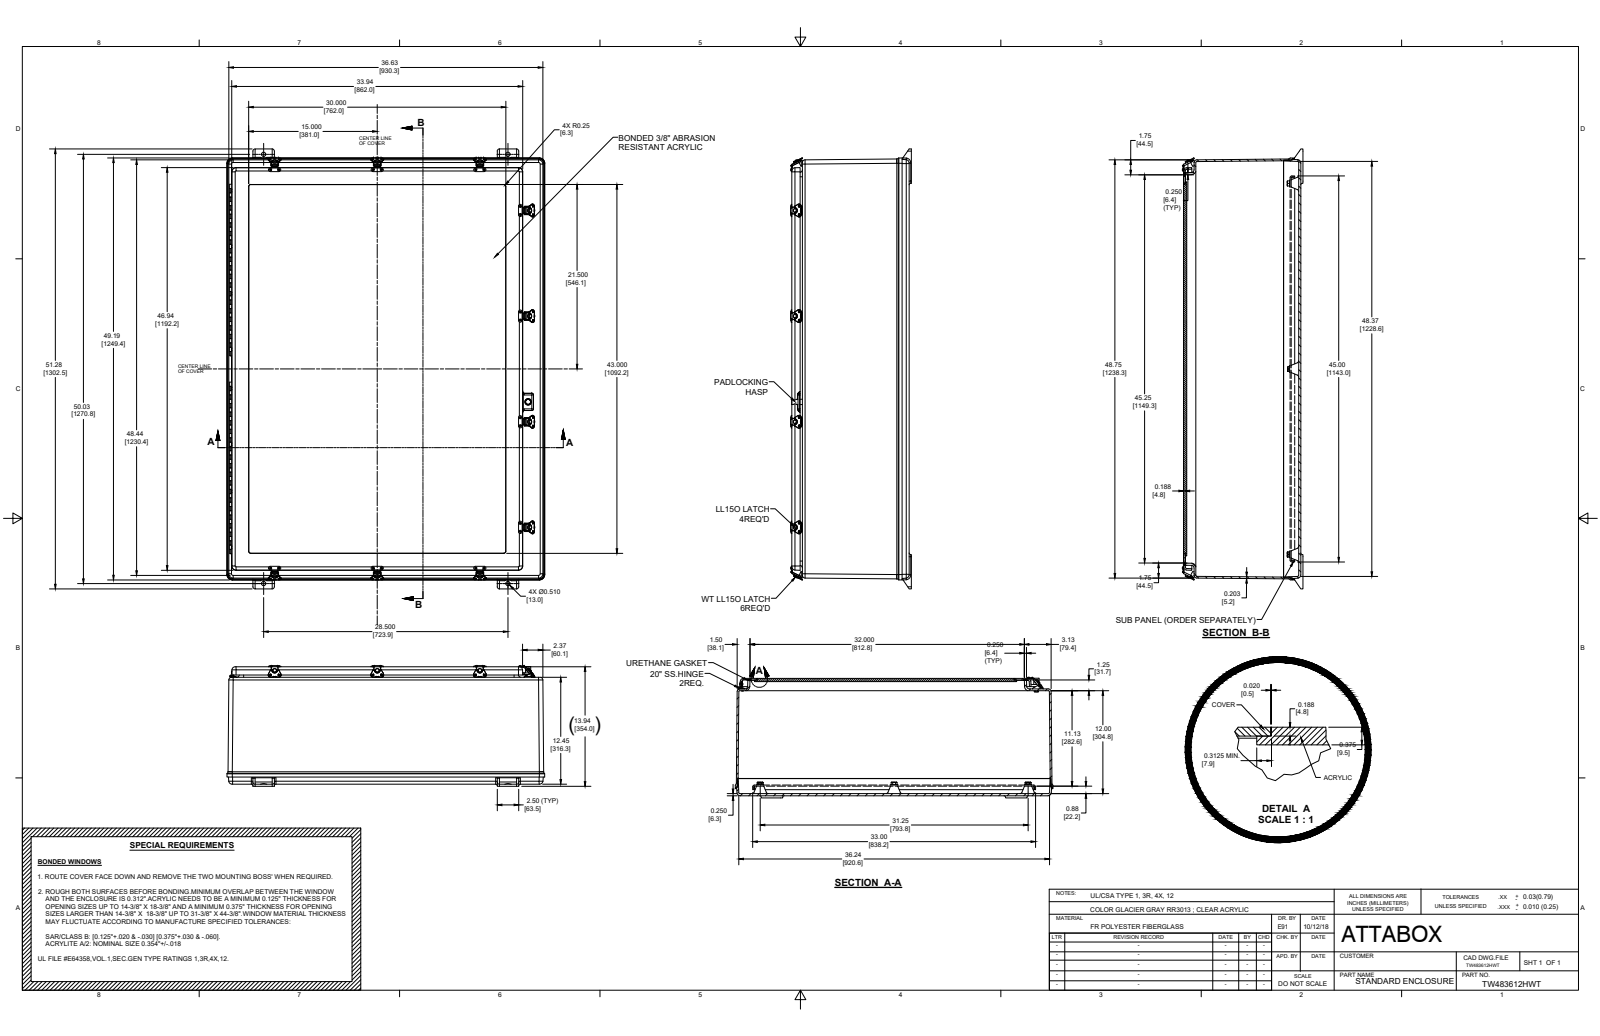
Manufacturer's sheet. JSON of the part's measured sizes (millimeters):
{"part_name": "TW483612HWT", "step_written_by": "SolidWorks 2018 (AUTOMOTIVE_DESIGN)", "units": "millimeters", "bodies": {"solids": 128, "faces": 3172, "planar": 1182, "cylindrical": 1248, "other": 742}, "overall_size": [1302.5, 941.4, 357.4], "volume_mm3": 25780000, "surface_area_mm2": 8438000, "round_holes": [[3.3, 76], [1.6, 40], [3.5, 20], [4.7, 20], [1.7, 8], [1.7, 8], [7.8, 8], [11, 4], [14.3, 4], [3.4, 3], [4, 3], [12.7, 2]], "round_bosses_or_shafts": [[3.6, 40], [7.5, 16], [12.7, 10], [14.3, 4], [5.1, 3], [3.4, 2], [6.4, 1], [5.1, 1]], "partial_cylinders_radius": [[0.3, 217], [0.8, 40], [7.9, 34], [6.4, 28], [5.3, 20], [30.1, 20], [4.7, 18], [9.5, 18]], "face_to_face_distances": [6.4, 347.4, 341, 337.9, 331.5, 9.5, 5.2, 5.2, 4.8, 4.7], "hole_center_spacings": [25.4, 165.1, 304, 304.8, 1253.1, 312.8, 12.7, 1215.6]}
